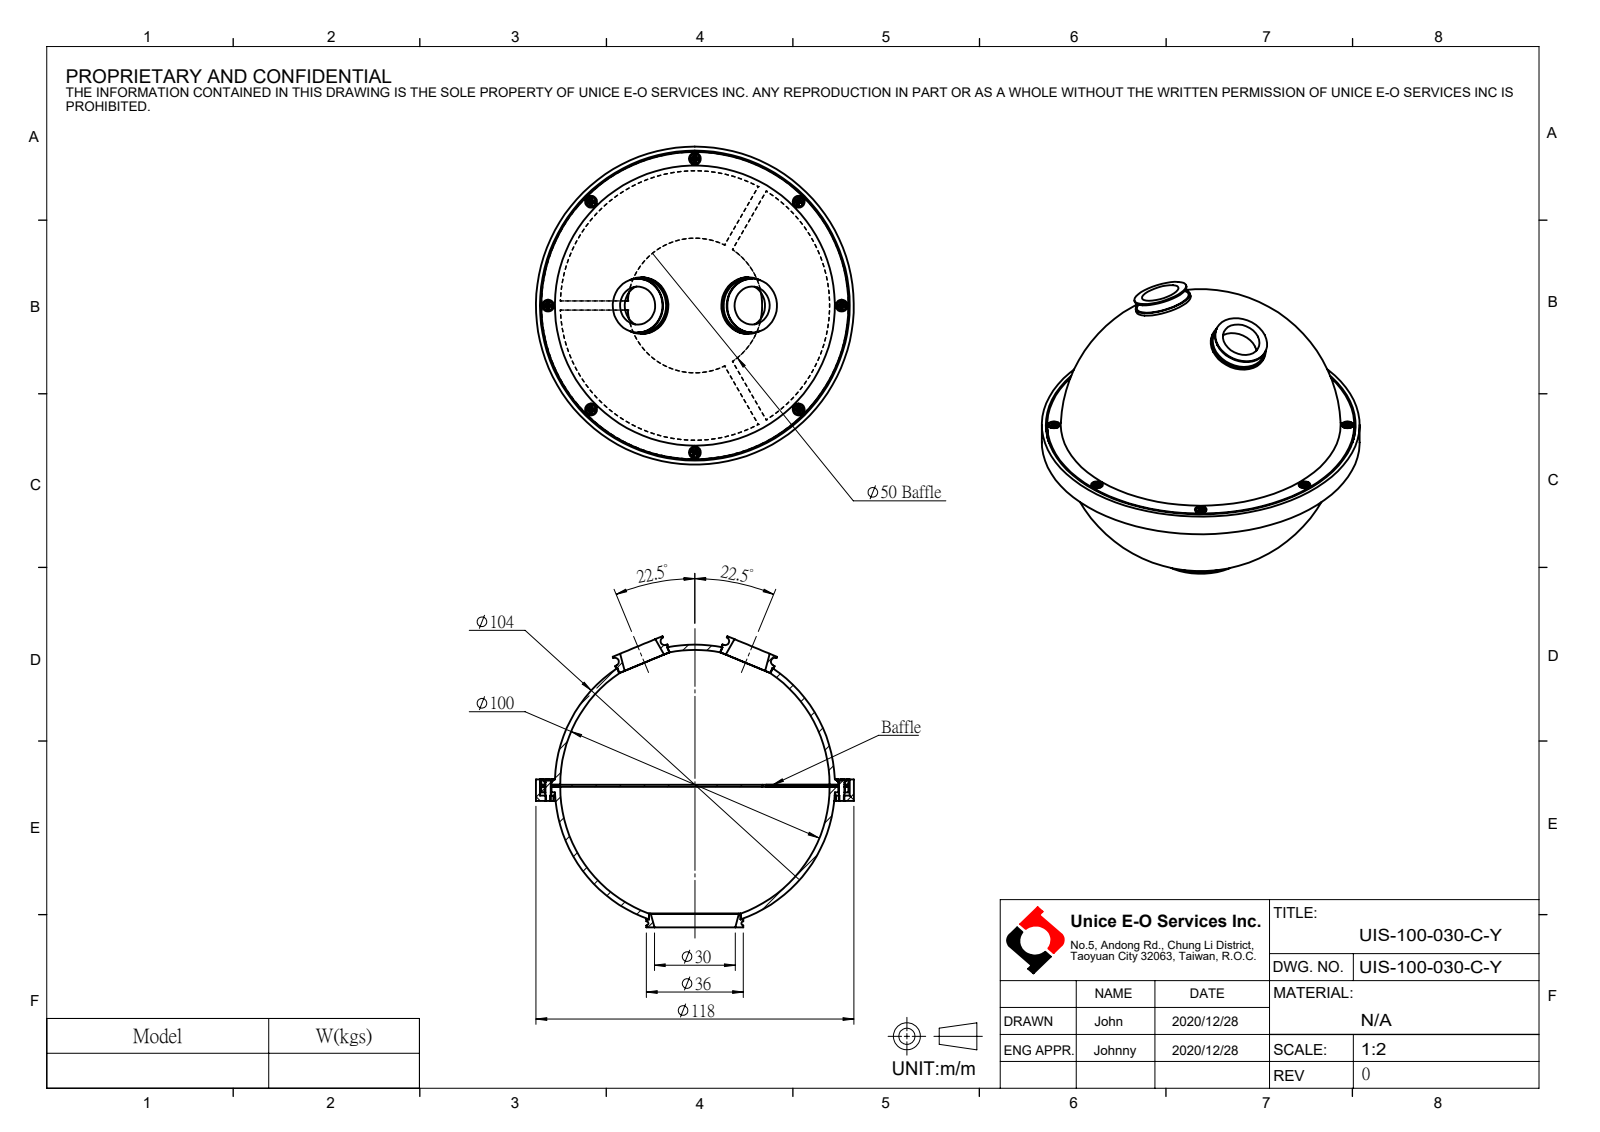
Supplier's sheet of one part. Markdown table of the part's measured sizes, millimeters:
| quantity | value |
| --- | --- |
| part name | UIS-100-030-C-Y |
| STEP written by | SolidWorks 2020 (CONFIG_CONTROL_DESIGN) |
| units | millimeters |
| bodies | 0 solids, 145 faces (51 planar, 38 cylindrical, 56 other) |
| overall size | 118 × 118 × 108.07 |
| round holes (diameter × count) | 105 × 1, 115 × 1 |
| round bosses / shafts (diameter × count) | 3.5 × 8, 21 × 2, 20 × 2, 118 × 1, 114 × 1, 36 × 1 |
| main face-to-face distances | 6, 2, 8, 4, 3.2, 1.2, 2.8, 4.8, 46.94, 48.94 |
